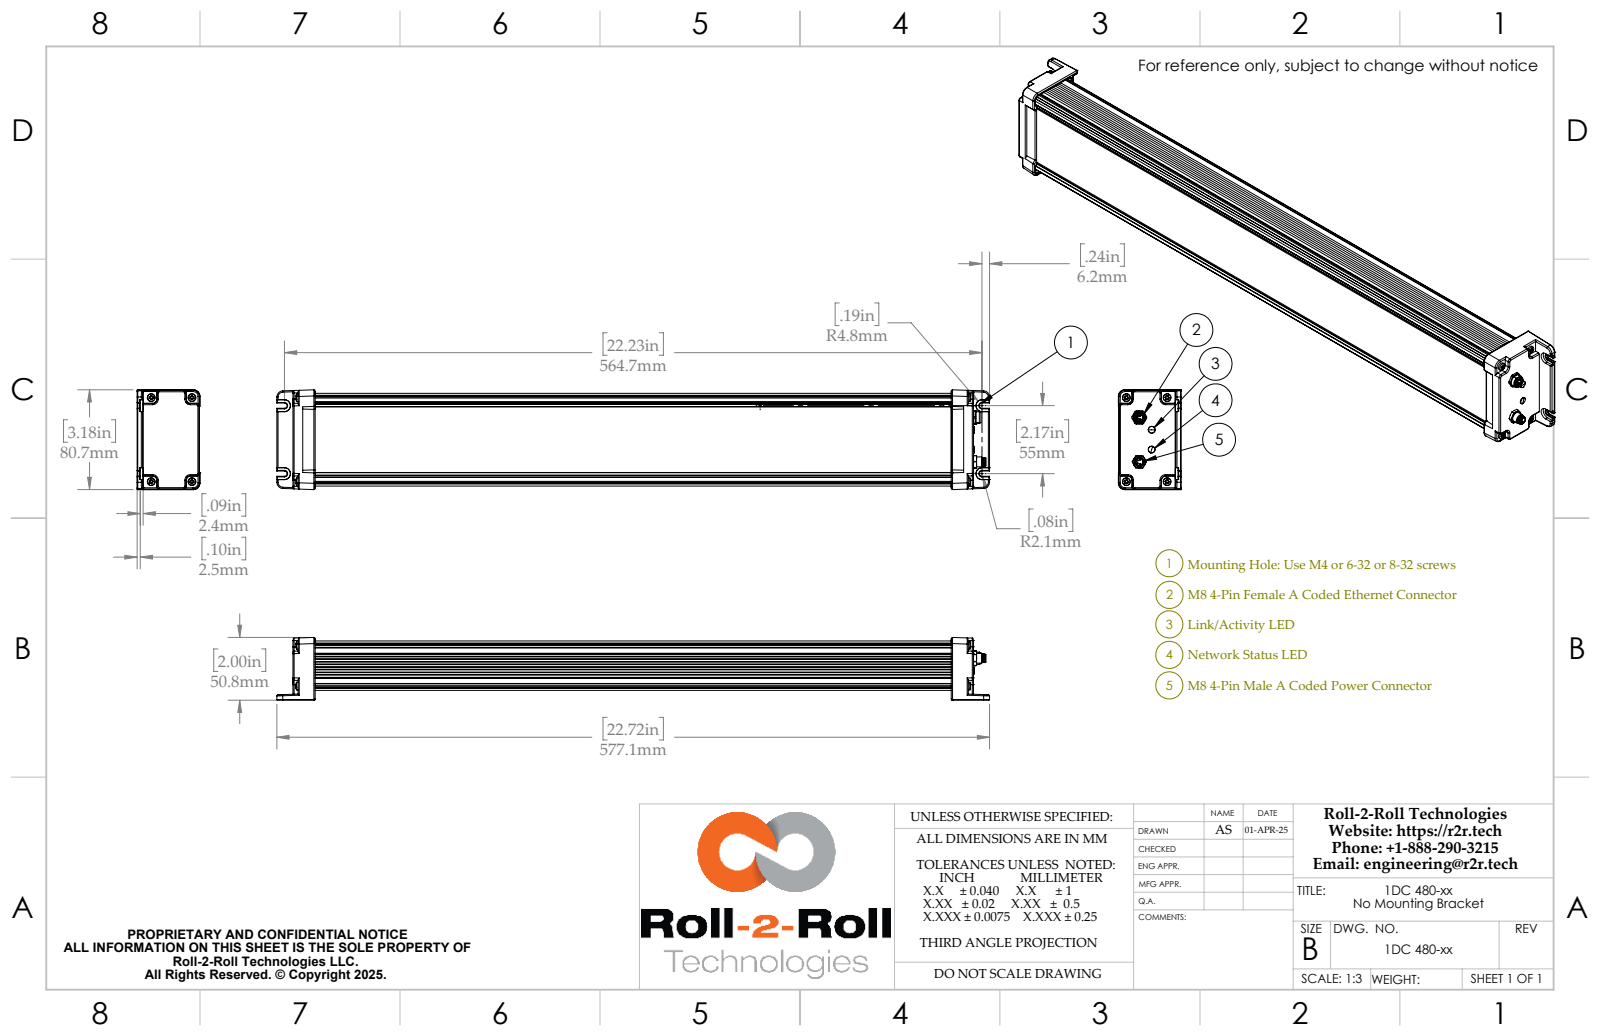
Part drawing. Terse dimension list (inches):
name: 1DC 480-xx
written by: SolidWorks 2017 (CONFIG_CONTROL_DESIGN)
unit: in
bodies: 19 solids, 1466 faces (555 planar, 547 cylindrical, 364 other)
size: 22.719 × 3.178 × 1.998
volume: 29.43 in³; area: 588 in²
holes: 4× ⌀0.041, 1× ⌀0.228, 1× ⌀0.232, 1× ⌀0.291
bosses: 4× ⌀0.118, 4× ⌀0.098, 4× ⌀0.043, 4× ⌀0.039, 4× ⌀0.031, 2× ⌀0.191, 1× ⌀0.354, 1× ⌀0.35
rounds: 106× R0.02, 72× R0.039, 48× R0.079, 20× R0.012, 10× R0.035, 9× R0.197, 8× R0.044, 8× R0.047
face distances: 0.079, 1.299, 1.378, 1.22, 0.159, 1.458, 1.379, 0.08, 0.167, 0.098
hole spacings: 0.07, 0.081, 0.133, 0.071, 0.071, 0.085, 0.134, 1.35
